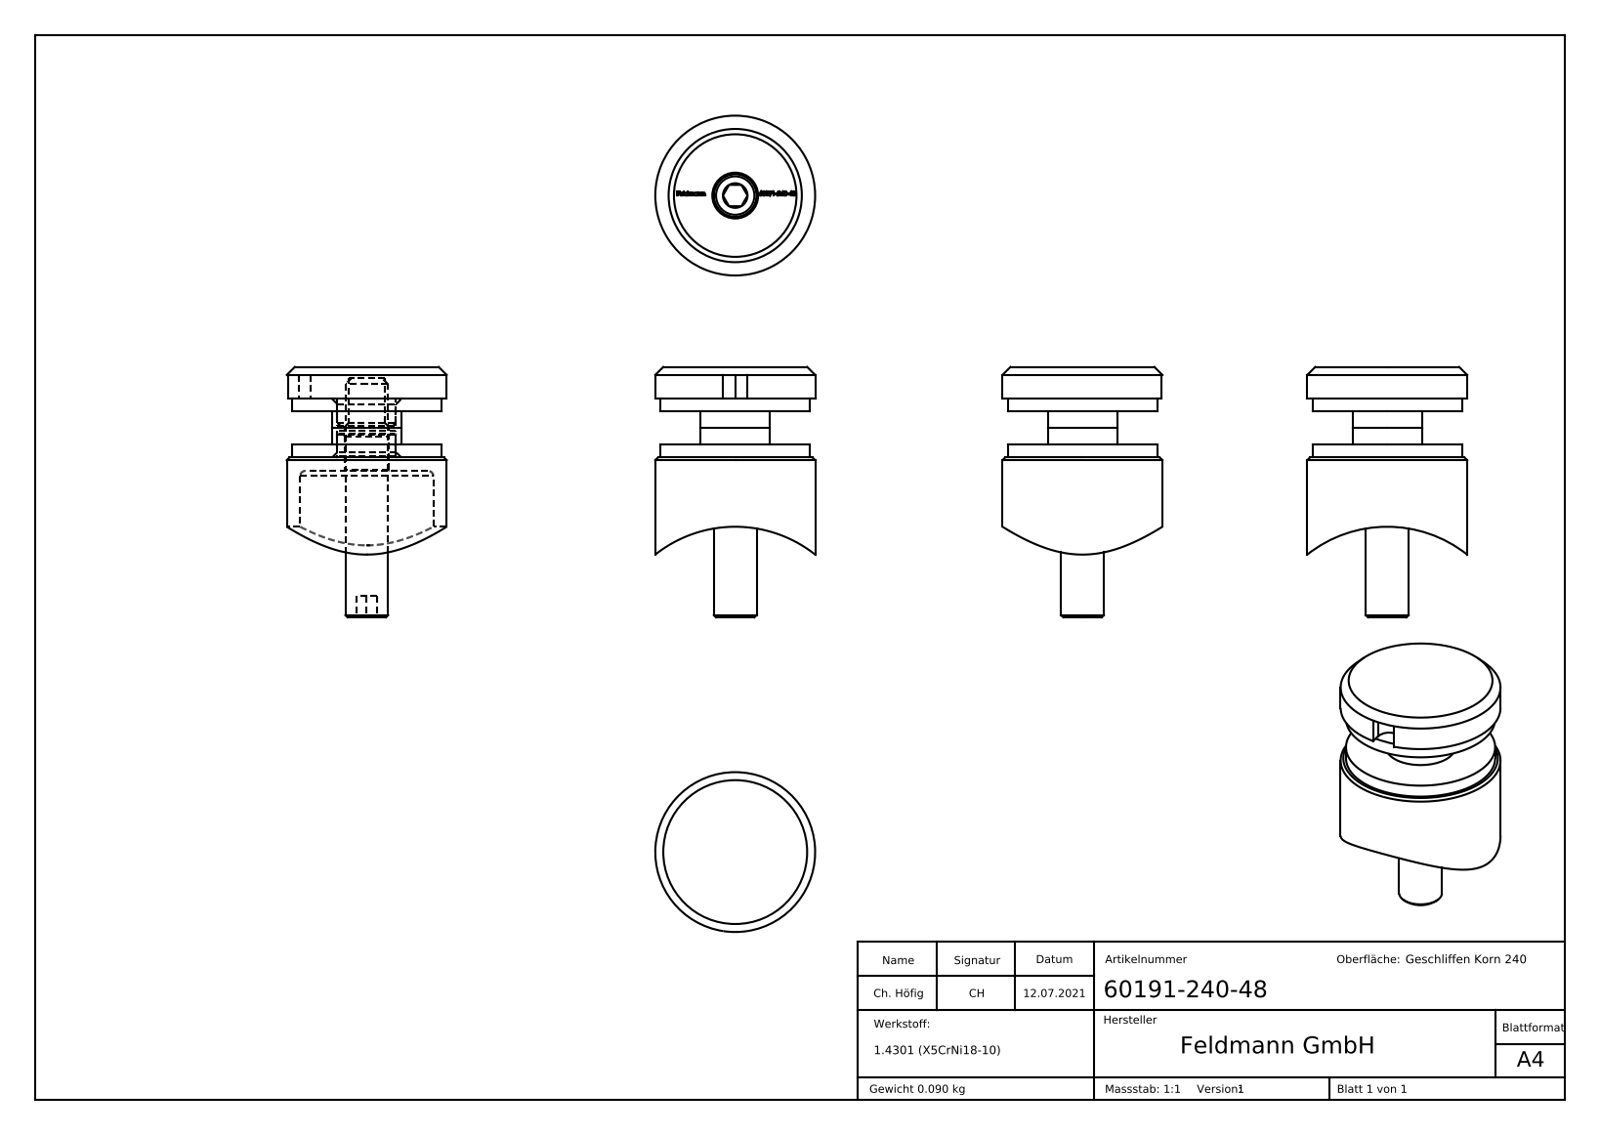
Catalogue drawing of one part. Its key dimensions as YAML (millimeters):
part_name: "60190-240 Teil2_60191-240-48 Teil2; DIN913 M8x45; 60190-240 Teil2; 6019X-240 Teil3_6019X-240 Teil3 (+5 more)"
step_written_by: "SolidWorks 2018 (CONFIG_CONTROL_DESIGN)"
units: millimeters
bodies: {solids: 5, faces: 340, planar: 170, cylindrical: 35, other: 135}
overall_size: [47, 30, 30]
volume: 13676
surface_area: 10809
round_holes:
  - {diameter: 6.8, count: 1}
  - {diameter: 8.2, count: 1}
  - {diameter: 11, count: 1}
  - {diameter: 25, count: 1}
round_bosses_or_shafts:
  - {diameter: 30, count: 1}
  - {diameter: 28, count: 1}
  - {diameter: 13, count: 1}
  - {diameter: 8, count: 1}
partial_cylinders:
  - {radius: 2.25, count: 1}
  - {radius: 24.15, count: 1}
face_to_face_distances: [11, 2.4, 8.6, 6, 17, 8.4, 6.2, 14.6, 2.5, 4.9]
